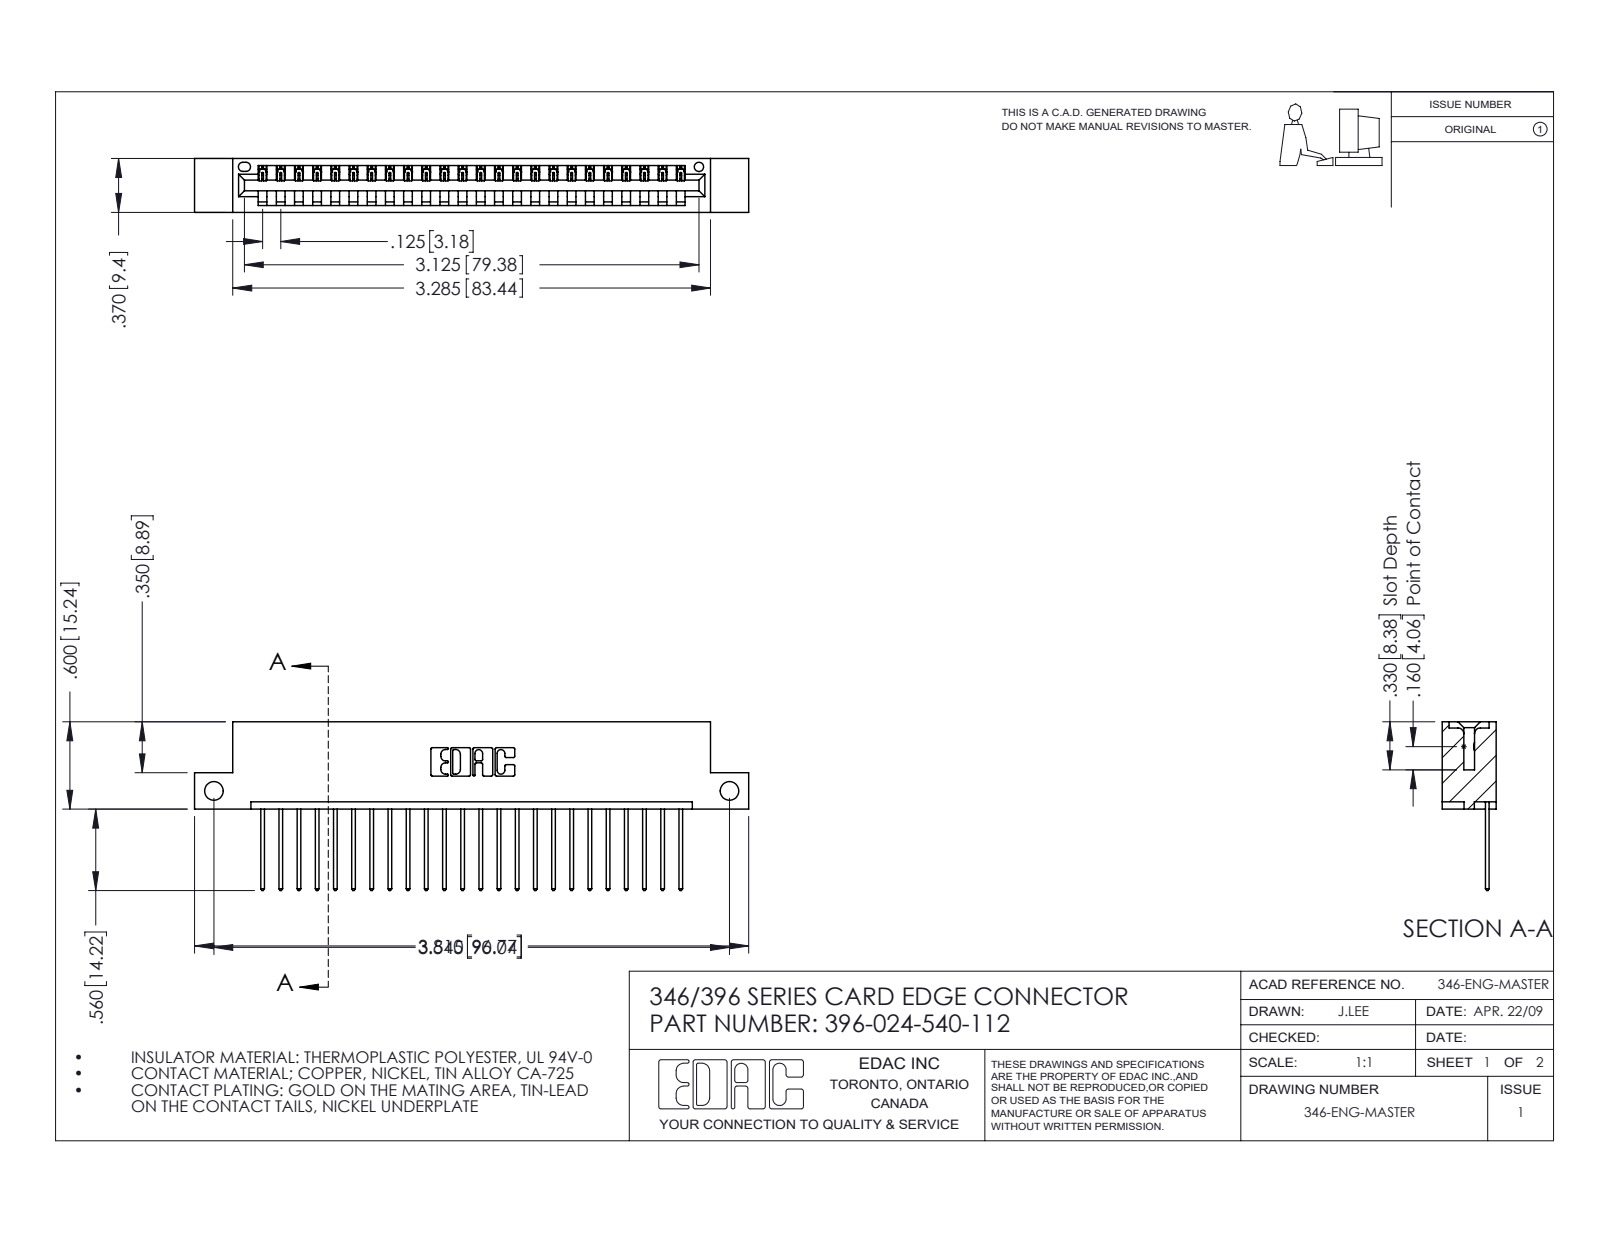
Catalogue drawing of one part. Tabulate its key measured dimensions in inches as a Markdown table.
| quantity | value |
| --- | --- |
| part name | 396-024-540-112; 345-292-001_345-293-140; 346 Part_Flush Mounting Lugs - Side Mount |
| STEP written by | SolidWorks 2016 (CONFIG_CONTROL_DESIGN) |
| units | inches |
| bodies | 25 solids, 1514 faces (1036 planar, 478 cylindrical, 0 other) |
| overall size | 3.81 × 1.16 × 0.37 |
| volume | 0.554 in³ |
| surface area | 17.44 in² |
| round holes (diameter × count) | 0.128 × 2, 0.064 × 1 |
| partial cylindrical surfaces (radius × count) | 0.006 × 48, 0.01 × 48, 0.01 × 22, 0.007 × 6, 0.031 × 6, 0.026 × 3, 0.031 × 2, 0.04 × 2 |
| main face-to-face distances | 0.048, 0.322, 0.25, 0.37, 0.072, 0.298, 0.025, 0.148, 0.222, 0.1 |
| hole center spacings | 3.545 |
